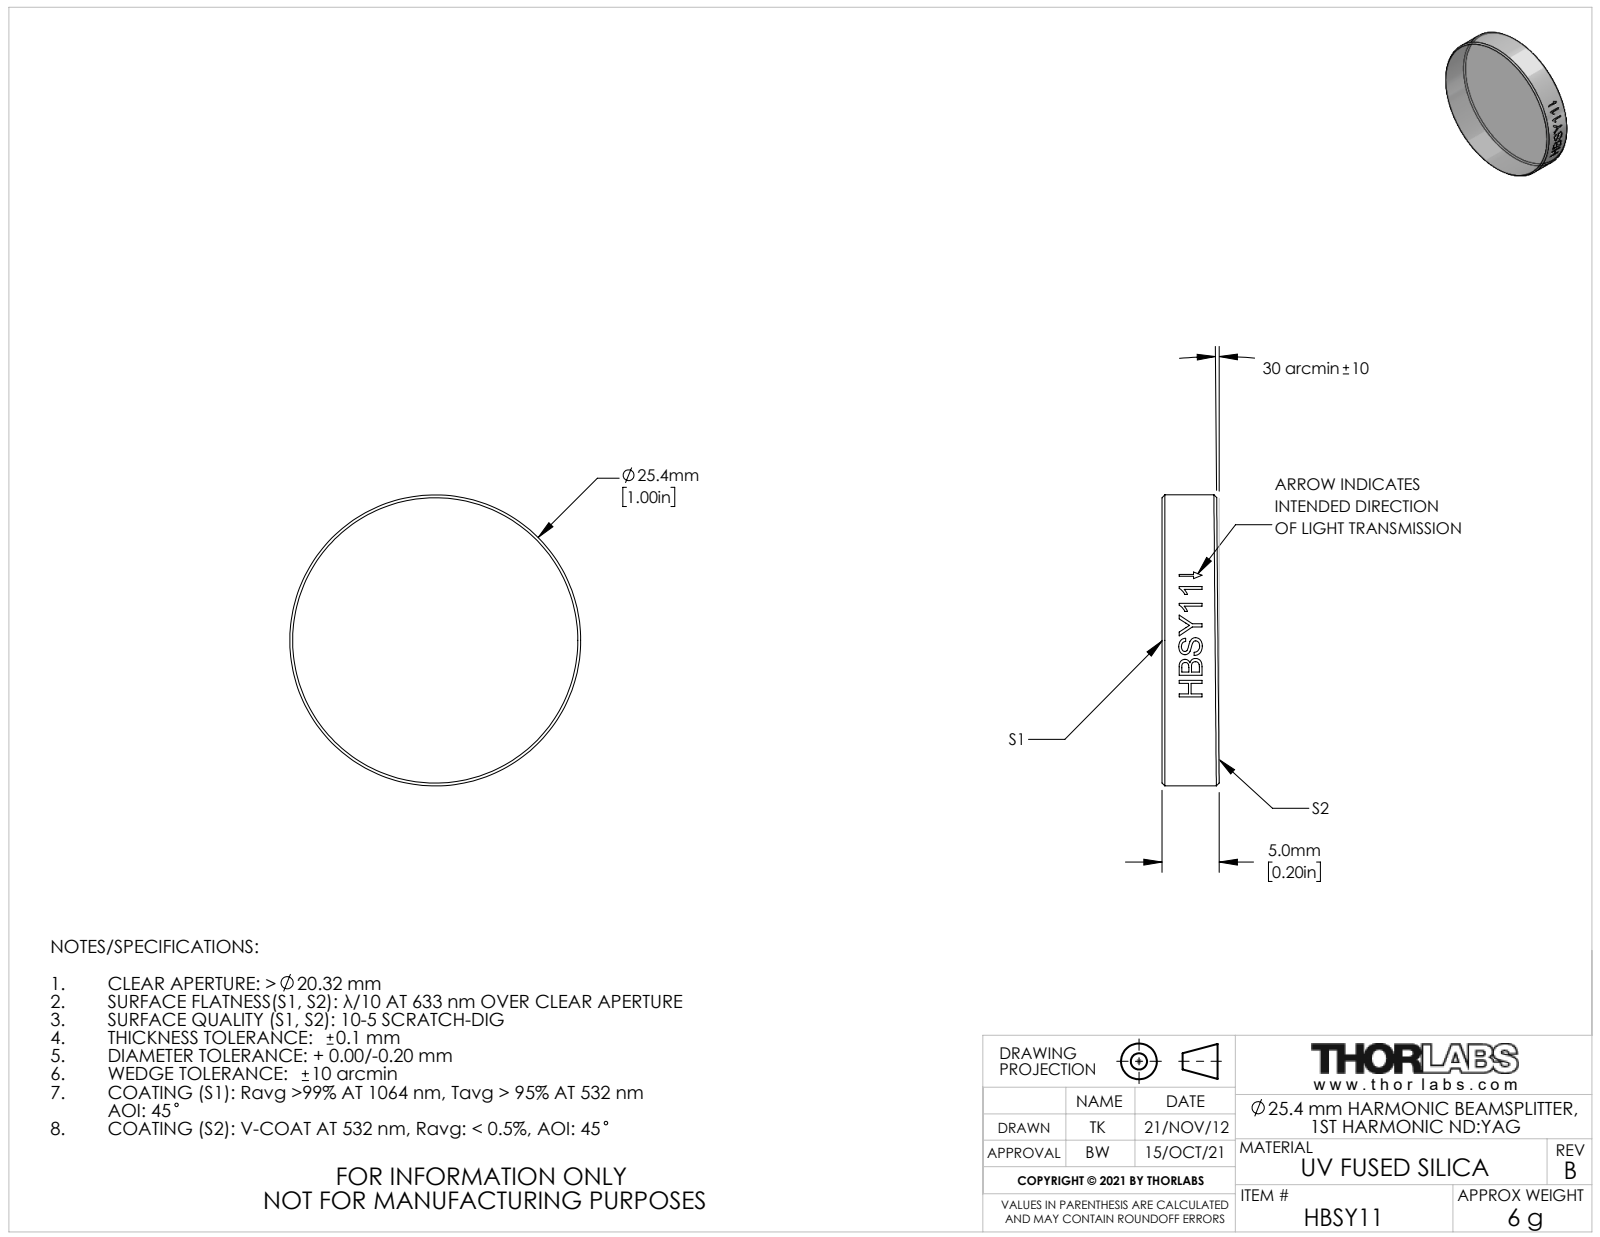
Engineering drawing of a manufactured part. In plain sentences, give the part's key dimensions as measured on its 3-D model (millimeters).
The part is named "TTN006422-E0W". Its 3-D file was written by "SolidWorks 2012 (CONFIG_CONTROL_DESIGN)". It is 1 solid with 18 faces: 2 planar, 12 cylindrical and 4 other. Overall it measures 25.4 by 25.4 by 5 millimeters. Its volume is 2 472 cubic millimeters and its surface area 1 380 square millimeters. Round bosses or shafts: 1 of diameter 25.4.
